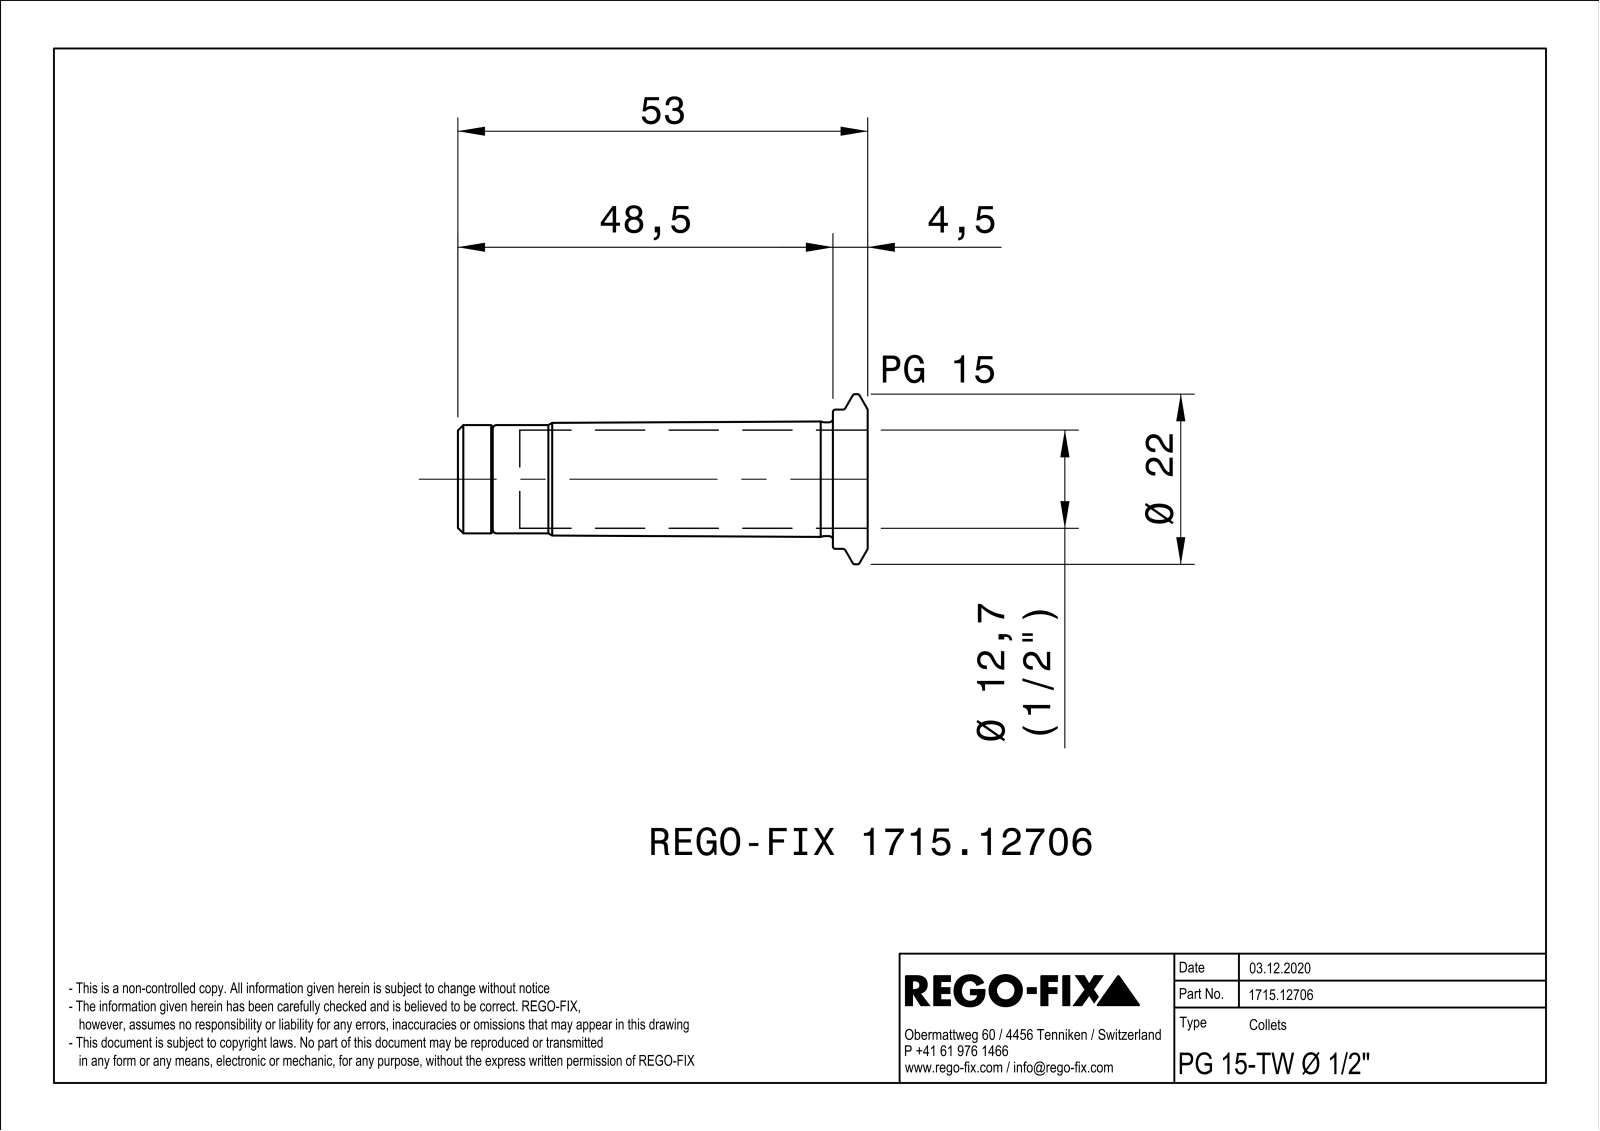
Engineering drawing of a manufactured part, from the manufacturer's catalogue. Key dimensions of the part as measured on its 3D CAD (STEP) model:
Part name (STEP PRODUCT): NOCUT
STEP written by: SIEMENS PLM Software Solid Edge ST10 (AUTOMOTIVE_DESIGN)
Units: millimetres
Bodies: 2 solids, 59 faces (24 planar, 17 cylindrical, 18 other)
Overall size (bounding box): 53 × 22 × 22
Volume: 3 320 mm³ · Surface area: 5 450 mm²
Round holes (diameter × count): ⌀5.2 ×1, ⌀6.92 ×1, ⌀8.2 ×1, ⌀12.7 ×1, ⌀12.8 ×1, ⌀13 ×1
Round bosses / shafts (diameter × count): ⌀22 ×1, ⌀18 ×1, ⌀14.92 ×1, ⌀14.87 ×1, ⌀14 ×1, ⌀12.6 ×1, ⌀12 ×1
Main face-to-face distances: 1, 45, 53, 8, 4.5, 48.5, 3.5, 2.5, 46, 7
